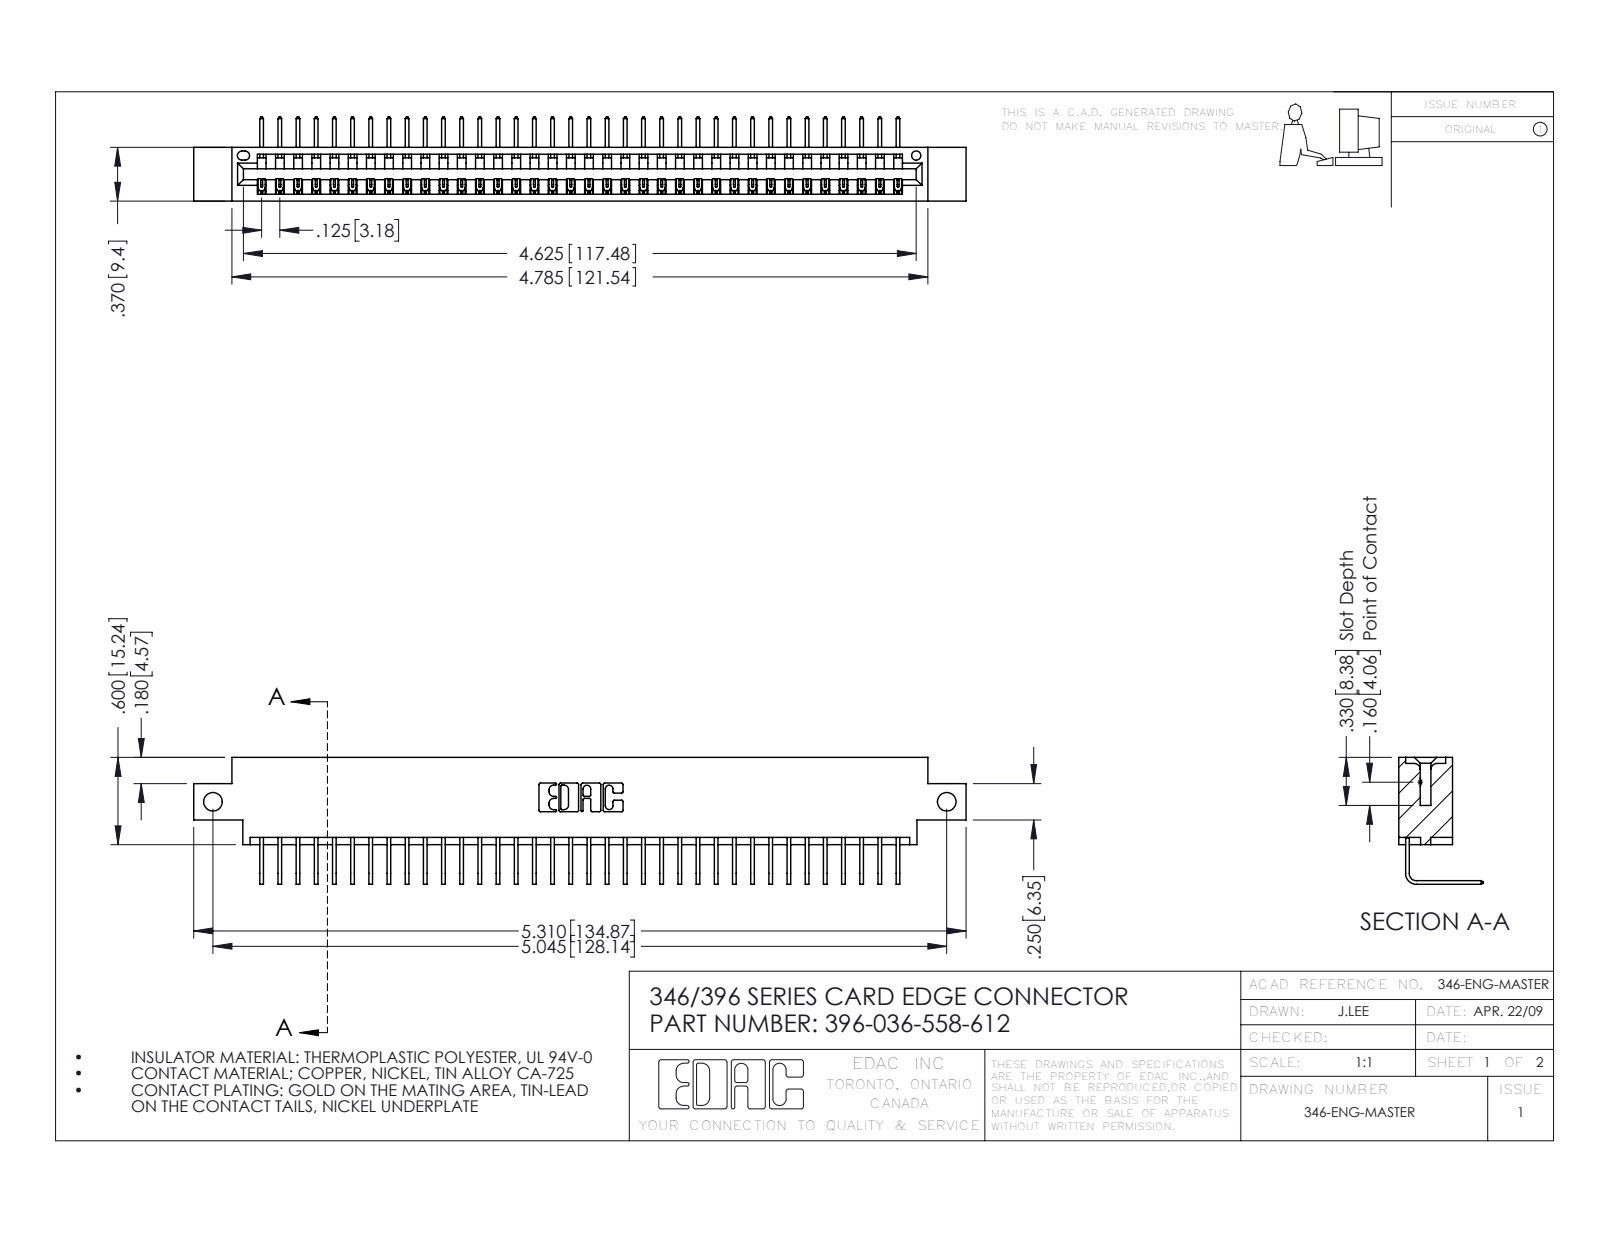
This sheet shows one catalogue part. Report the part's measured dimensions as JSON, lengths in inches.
{"part_name": "396-036-558-612; 345-292-001_558 Tail - 2; 346 Part_0.170 Offset - Side Mount", "step_written_by": "SolidWorks 2016 (CONFIG_CONTROL_DESIGN)", "units": "inches", "bodies": {"solids": 37, "faces": 2286, "planar": 1592, "cylindrical": 694, "other": 0}, "overall_size": [5.31, 0.873, 0.58], "volume_in3": 0.778, "surface_area_in2": 25.73, "round_holes": [[0.128, 2], [0.064, 1]], "partial_cylinders_radius": [[0.006, 72], [0.01, 22], [0.007, 6], [0.031, 6], [0.026, 3], [0.031, 2], [0.04, 2], [0.014, 1]], "face_to_face_distances": [0.322, 0.048, 0.37, 0.25, 0.298, 0.025, 0.072, 0.148, 0.222, 0.1], "hole_center_spacings": [5.045]}
